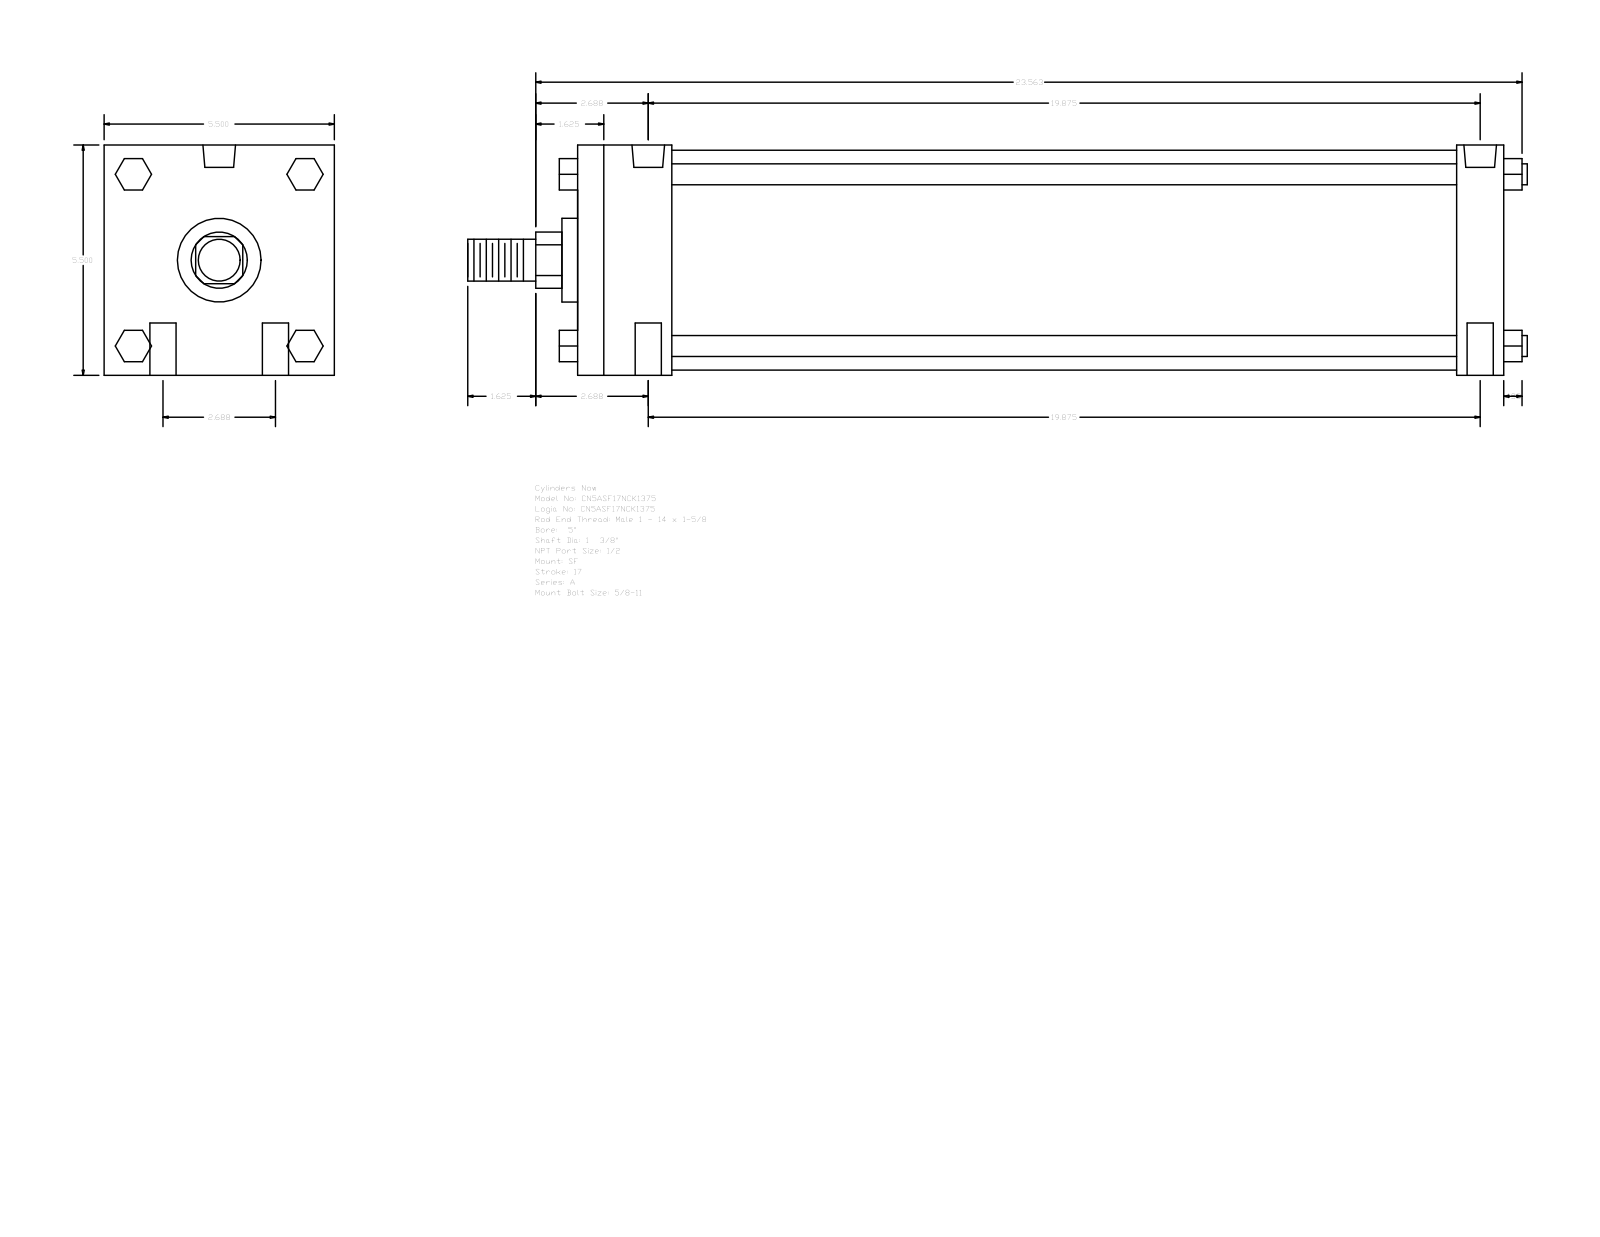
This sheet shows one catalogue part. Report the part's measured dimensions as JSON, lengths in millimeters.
{"part_name": "A_SF__0500_1.375", "step_written_by": "GSSL Pune (CONFIG_CONTROL_DESIGN)", "units": "millimeters", "bodies": {"solids": 0, "faces": 124, "planar": 94, "cylindrical": 30, "other": 0}, "overall_size": [642.94, 139.7, 139.7], "round_holes": [[15.88, 4], [8.73, 2], [19.77, 2]], "round_bosses_or_shafts": [[12.7, 4], [133.35, 1], [50.8, 1], [34.92, 1], [25.4, 1]], "partial_cylinders_radius": [[17.06, 1]], "face_to_face_distances": [139.7, 561.98, 57.15, 28.58, 533.4, 476.25, 504.83, 19.05, 52.07, 90.18], "hole_center_spacings": [34.13, 505.98, 504.83, 68.26, 509.42, 500.05]}
